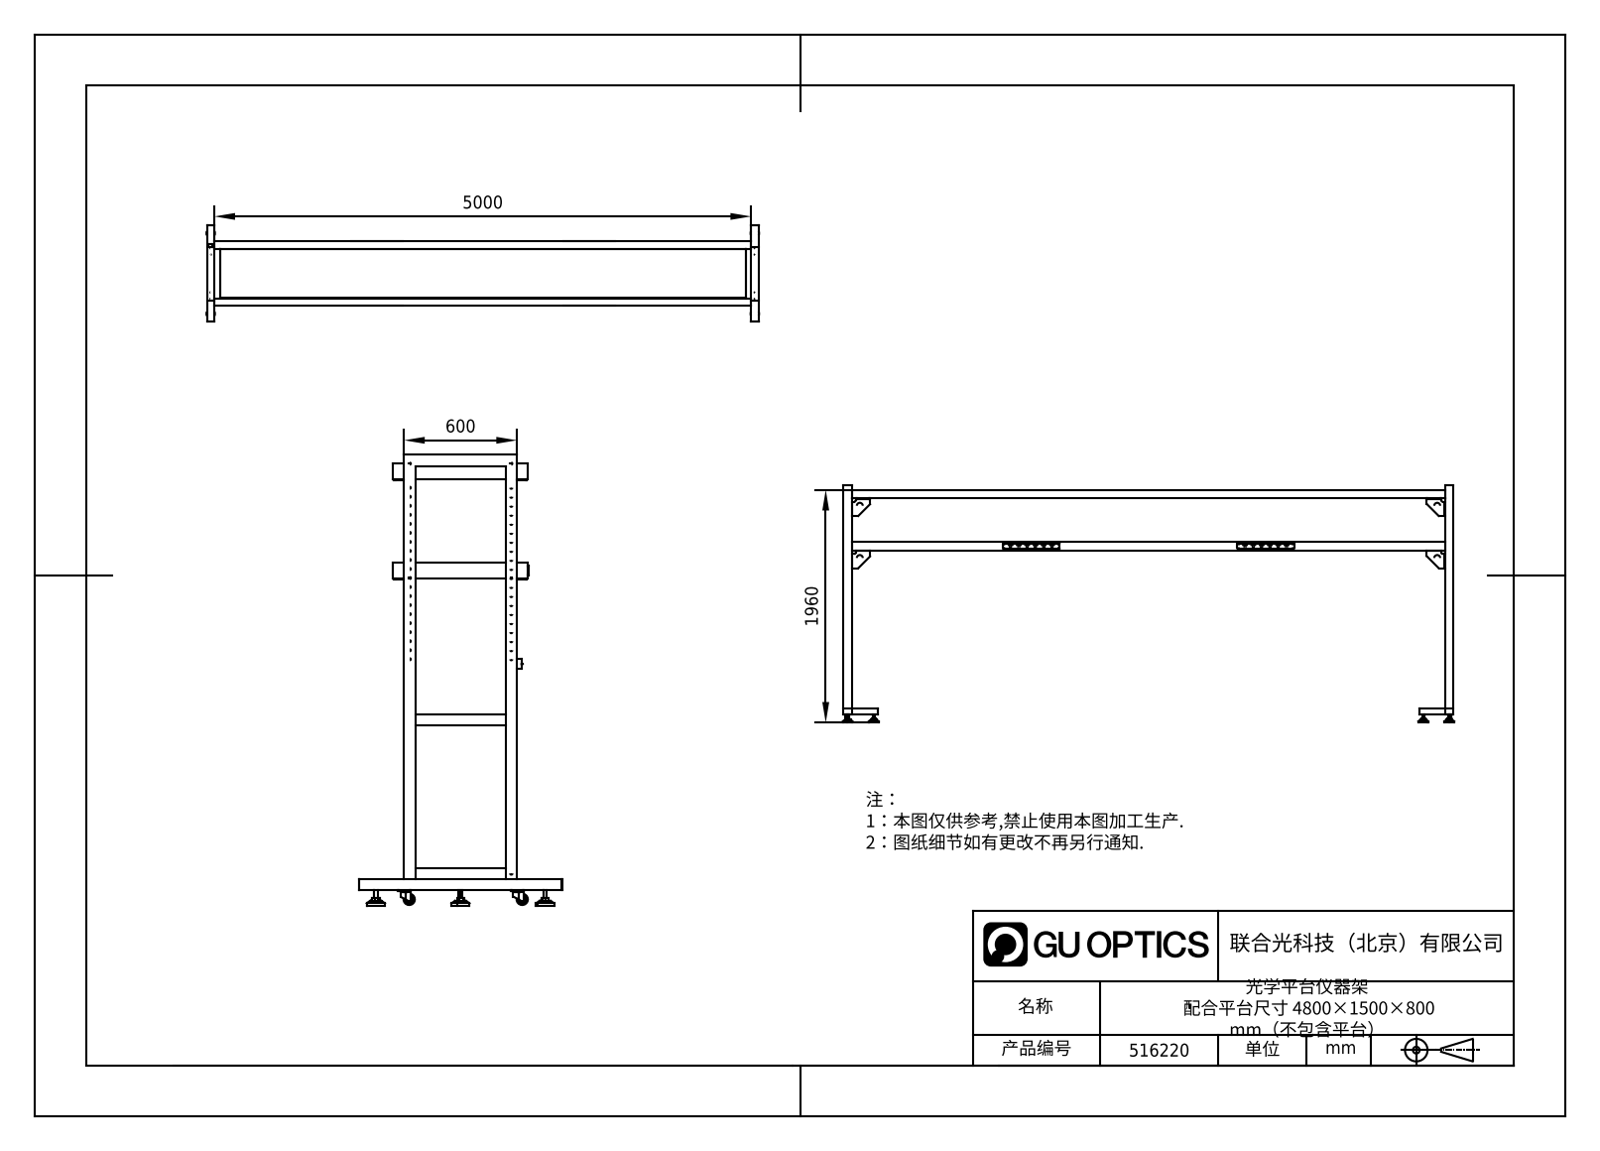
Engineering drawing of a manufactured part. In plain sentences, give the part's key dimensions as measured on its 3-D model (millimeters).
The part is named "516220". Its 3-D file was written by "SolidWorks 2020 (AUTOMOTIVE_DESIGN)". It is 55 solids with 2593 faces: 1445 planar, 1072 cylindrical and 76 other. Overall it measures 5150 by 2001 by 900 millimeters. Its volume is 35 990 000 cubic millimeters and its surface area 27 570 000 square millimeters. Round holes: 66 of diameter 9, 16 of diameter 6.1, 16 of diameter 10, 12 of diameter 6.5, 8 of diameter 4.2, 8 of diameter 5.2, 8 of diameter 6, 6 of diameter 17, 6 of diameter 18, 6 of diameter 26, 6 of diameter 69, 4 of diameter 3.2. Round bosses or shafts: 6 of diameter 80, 6 of diameter 16, 4 of diameter 26, 4 of diameter 18, 2 of diameter 50, 2 of diameter 10. Partial cylindrical surfaces (rounded edges, fillets, slot ends): 36 of radius 5, 24 of radius 7, 16 of radius 3, 12 of radius 4.25, 8 of radius 1.5, 8 of radius 1.51, 8 of radius 4.01, 4 of radius 13. The main face-to-face distances are 440, 1.5, 3, 70, 67, 438.5, 2.5, 67.5, 441.5, 530. The hole center spacings are 40, 80, 120, 280, 160, 200, 240, 320.
